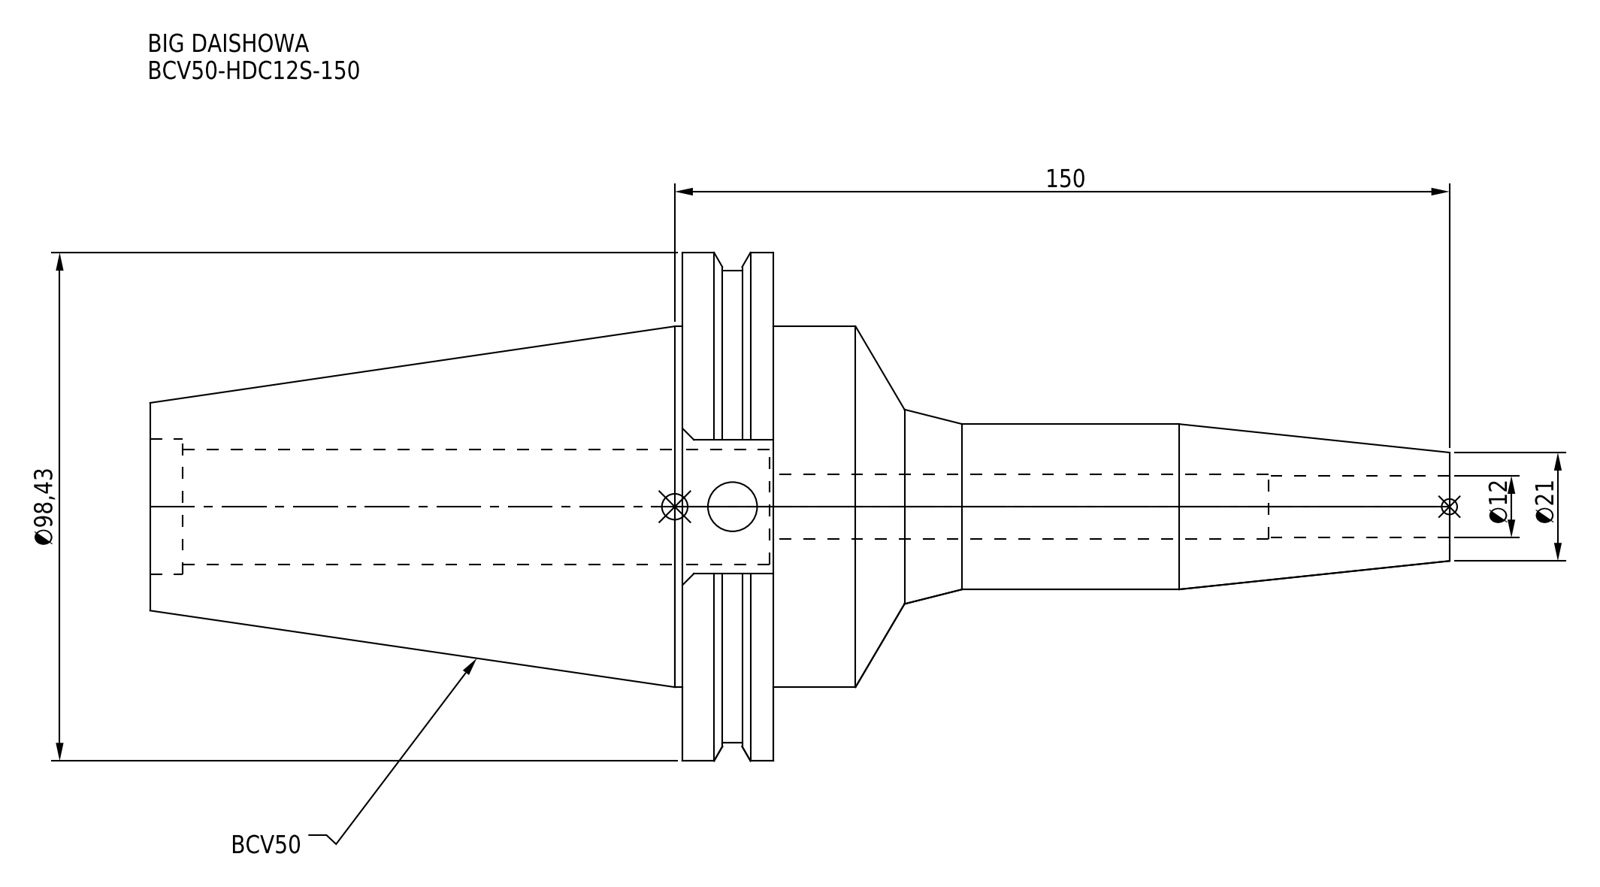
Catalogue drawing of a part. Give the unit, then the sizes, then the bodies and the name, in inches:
Units: inches
Overall size (bounding box): 9.906 × 3.875 × 3.738
Round holes (diameter × count): ⌀0.375 ×1, ⌀0.472 ×1, ⌀0.492 ×1, ⌀0.878 ×1, ⌀1.033 ×1
Round bosses / shafts (diameter × count): ⌀3.875 ×1, ⌀3.594 ×1, ⌀2.75 ×1, ⌀1.26 ×1
Main face-to-face distances: 0.691, 4.75, 4.059, 2.872, 1.02, 0.026, 0.665, 4.724, 5.156, 5.181
Volume: 28.34 in³ · Surface area: 97.65 in²
Bodies: 1 solid, 58 faces (22 planar, 24 cylindrical, 12 other)
Part name (STEP PRODUCT): BCV50-HDC12S-150
STEP written by: CREO PARAMETRIC BY PTC INC, 2016380 (AUTOMOTIVE_DESIGN)
